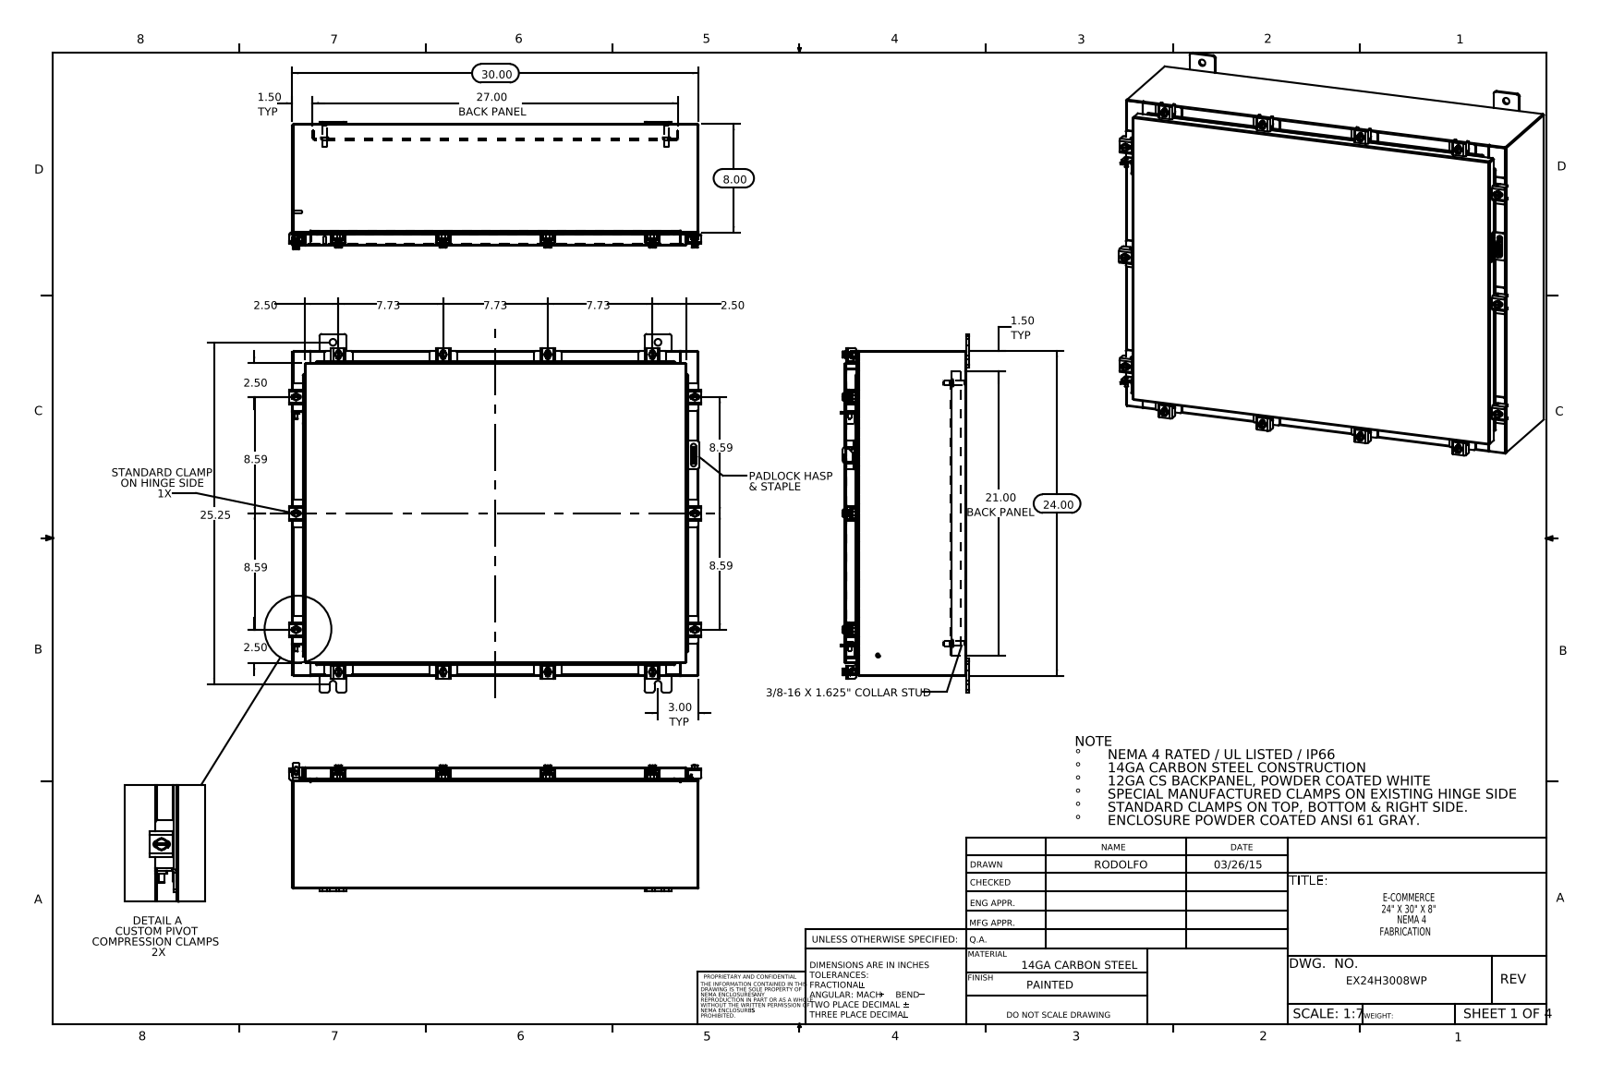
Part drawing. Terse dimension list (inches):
name: EX24H3008WP Mounting Studs; EX24H3008WP Top; EX24H3008WP Clamp Bracket; EX24H3008WP (+8 more)
written by: SolidWorks 2014 (CONFIG_CONTROL_DESIGN)
unit: in
bodies: 91 solids, 2252 faces (1195 planar, 881 cylindrical, 176 other)
size: 30.421 × 26.5 × 9.453
volume: 261.2 in³; area: 6 509 in²
holes: 14× ⌀0.213, 14× ⌀0.26, 8× ⌀0.5, 1× ⌀0.125, 1× ⌀0.25
bosses: 14× ⌀0.5, 14× ⌀0.25, 12× ⌀0.399, 4× ⌀0.625, 4× ⌀0.375, 4× ⌀0.33, 2× ⌀0.315, 2× ⌀0.236
rounds: 62× R0.06, 28× R0.141, 26× R0.12, 24× R0.013, 24× R0.19, 22× R0.088, 20× R0.09, 19× R0.05
face distances: 0.075, 8.9, 8.975, 8.826, 0.104, 1, 1.075, 7.826, 7.9, 1.179
hole spacings: 2.34, 4.429, 18.34, 20.559, 21.376, 23.451, 26.506, 33.251
